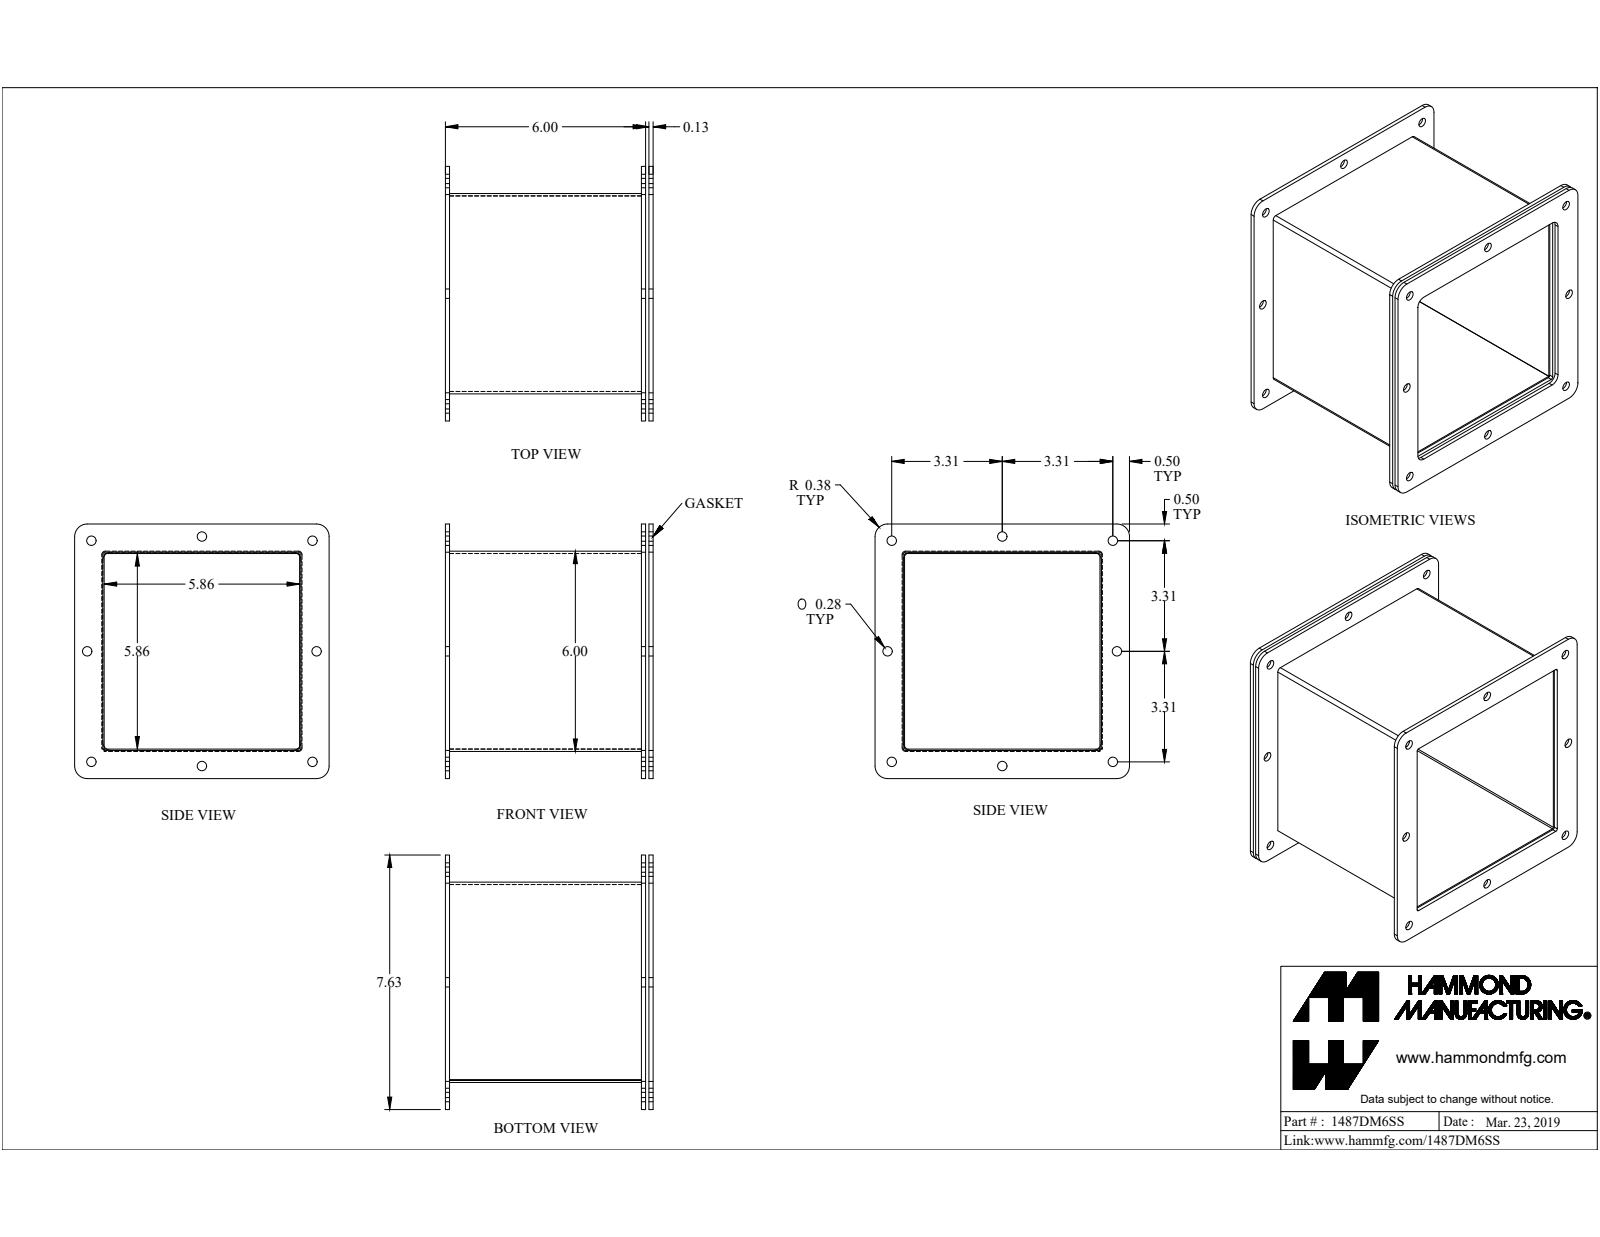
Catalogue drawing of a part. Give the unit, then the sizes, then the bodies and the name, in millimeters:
Units: millimetres
Overall size (bounding box): 193.7 × 193.7 × 166.9
Round holes (diameter × count): ⌀7.1 ×8, ⌀5 ×1, ⌀6.6 ×1, ⌀8.9 ×1
Round bosses / shafts (diameter × count): ⌀12.7 ×1, ⌀6.4 ×1
Partial cylindrical surfaces — rounded edges, fillets, slot ends (radius × count): R0.5 ×6, R1.6 ×4, R6.4 ×4, R9.5 ×4, R0.9 ×3, R2.7 ×3
Main face-to-face distances: 1.8, 150.6, 152.4, 3.2, 148.7, 5.7, 154.9, 149.2, 146.1, 2.5
Hole centre spacings: 84.2, 191, 123.5, 168.3, 174.6, 238
Volume: 298 200 mm³ · Surface area: 279 800 mm²
Bodies: 7 solids, 183 faces (99 planar, 76 cylindrical, 8 other)
Part name (STEP PRODUCT): 1487DM6SS
STEP written by: SolidWorks 2019 (CONFIG_CONTROL_DESIGN)
